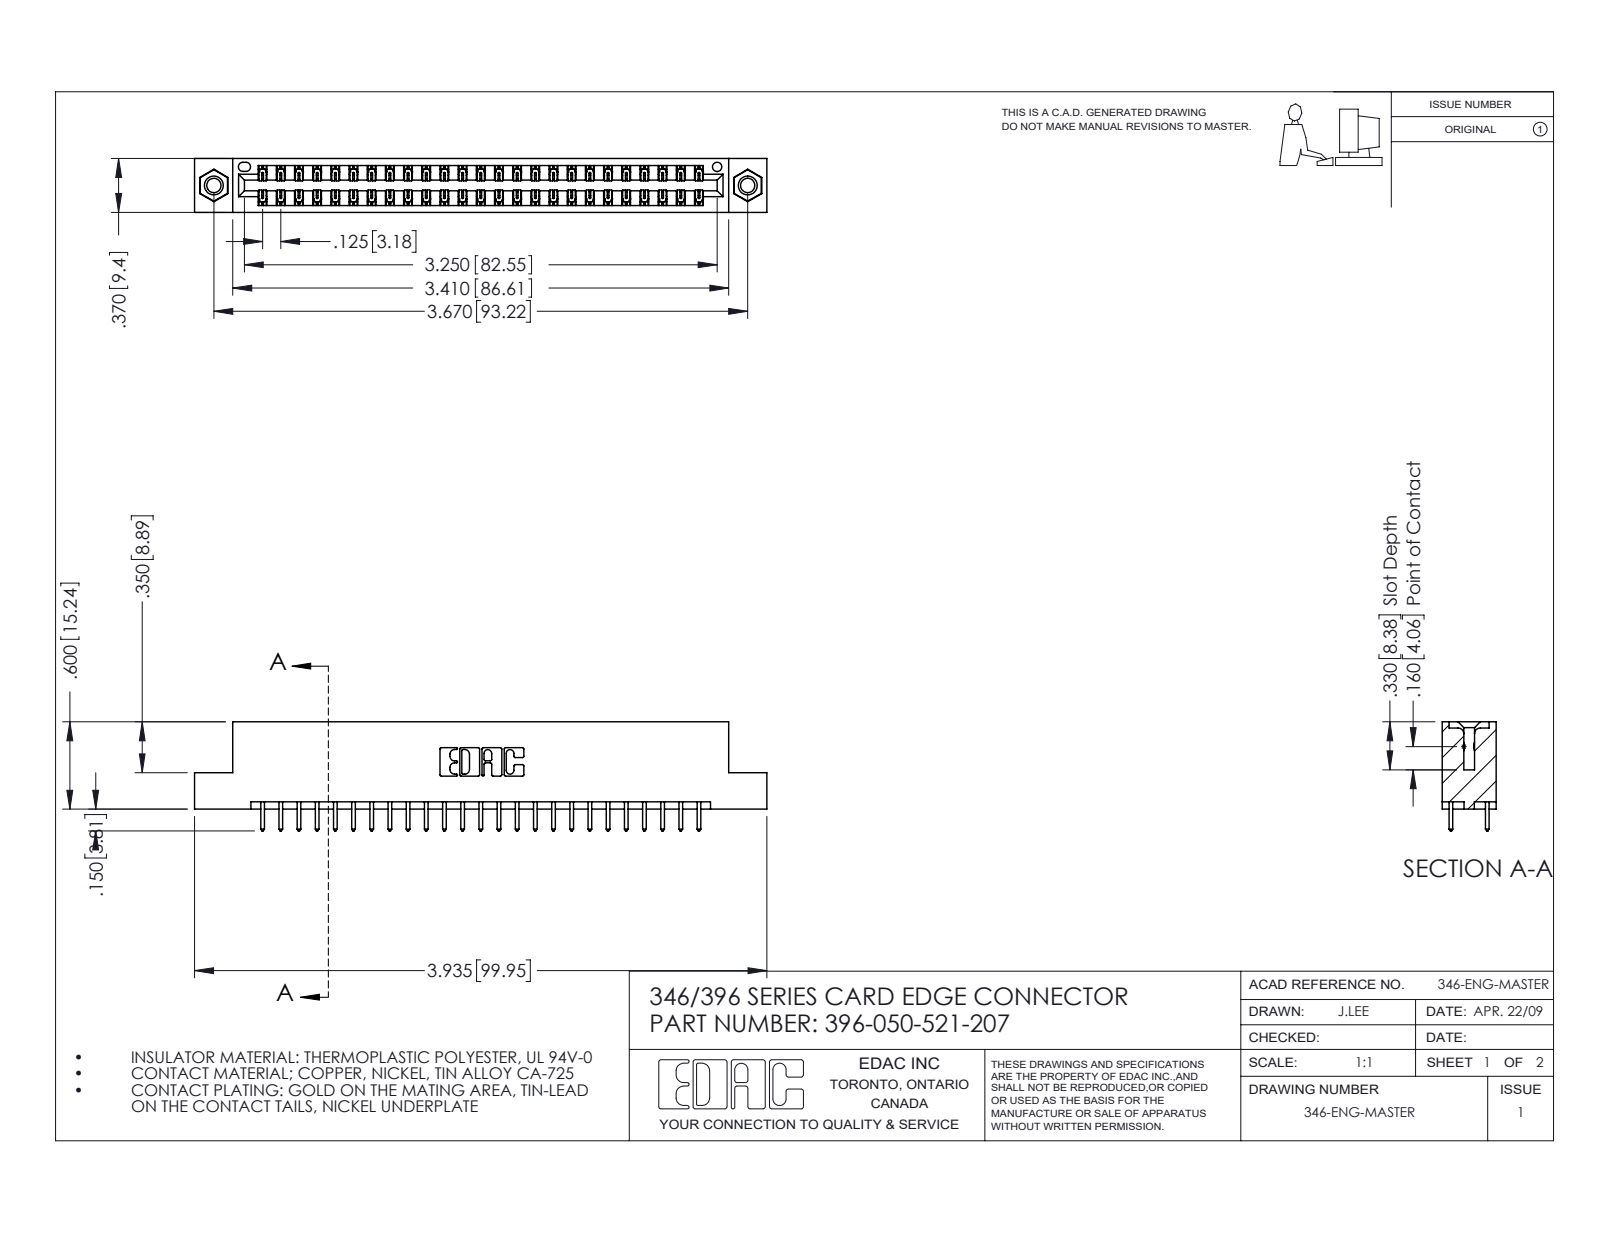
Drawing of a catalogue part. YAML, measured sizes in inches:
part_name: "396-050-521-207; 345-292-001_345-293-121; 346 Part_Flush Mounting Lugs - 0.156 Dia-TI; 345-250-001_345-250-005-103"
step_written_by: "SolidWorks 2016 (CONFIG_CONTROL_DESIGN)"
units: inches
bodies: {solids: 53, faces: 2782, planar: 1858, cylindrical: 908, other: 16}
overall_size: [3.935, 0.75, 0.37]
volume: 0.585
surface_area: 19.84
round_holes:
  - {diameter: 0.098, count: 2}
  - {diameter: 0.125, count: 2}
  - {diameter: 0.156, count: 2}
  - {diameter: 0.064, count: 1}
round_bosses_or_shafts:
  - {diameter: 0.155, count: 2}
partial_cylinders:
  - {radius: 0.006, count: 75}
  - {radius: 0.01, count: 50}
  - {radius: 0.01, count: 22}
  - {radius: 0.007, count: 6}
  - {radius: 0.031, count: 6}
  - {radius: 0.026, count: 3}
  - {radius: 0.014, count: 2}
  - {radius: 0.022, count: 2}
face_to_face_distances: [0.048, 0.322, 0.25, 0.37, 0.072, 0.298, 0.025, 0.275, 0.148, 0.222]
hole_center_spacings: [0.246, 3.462, 3.67]
